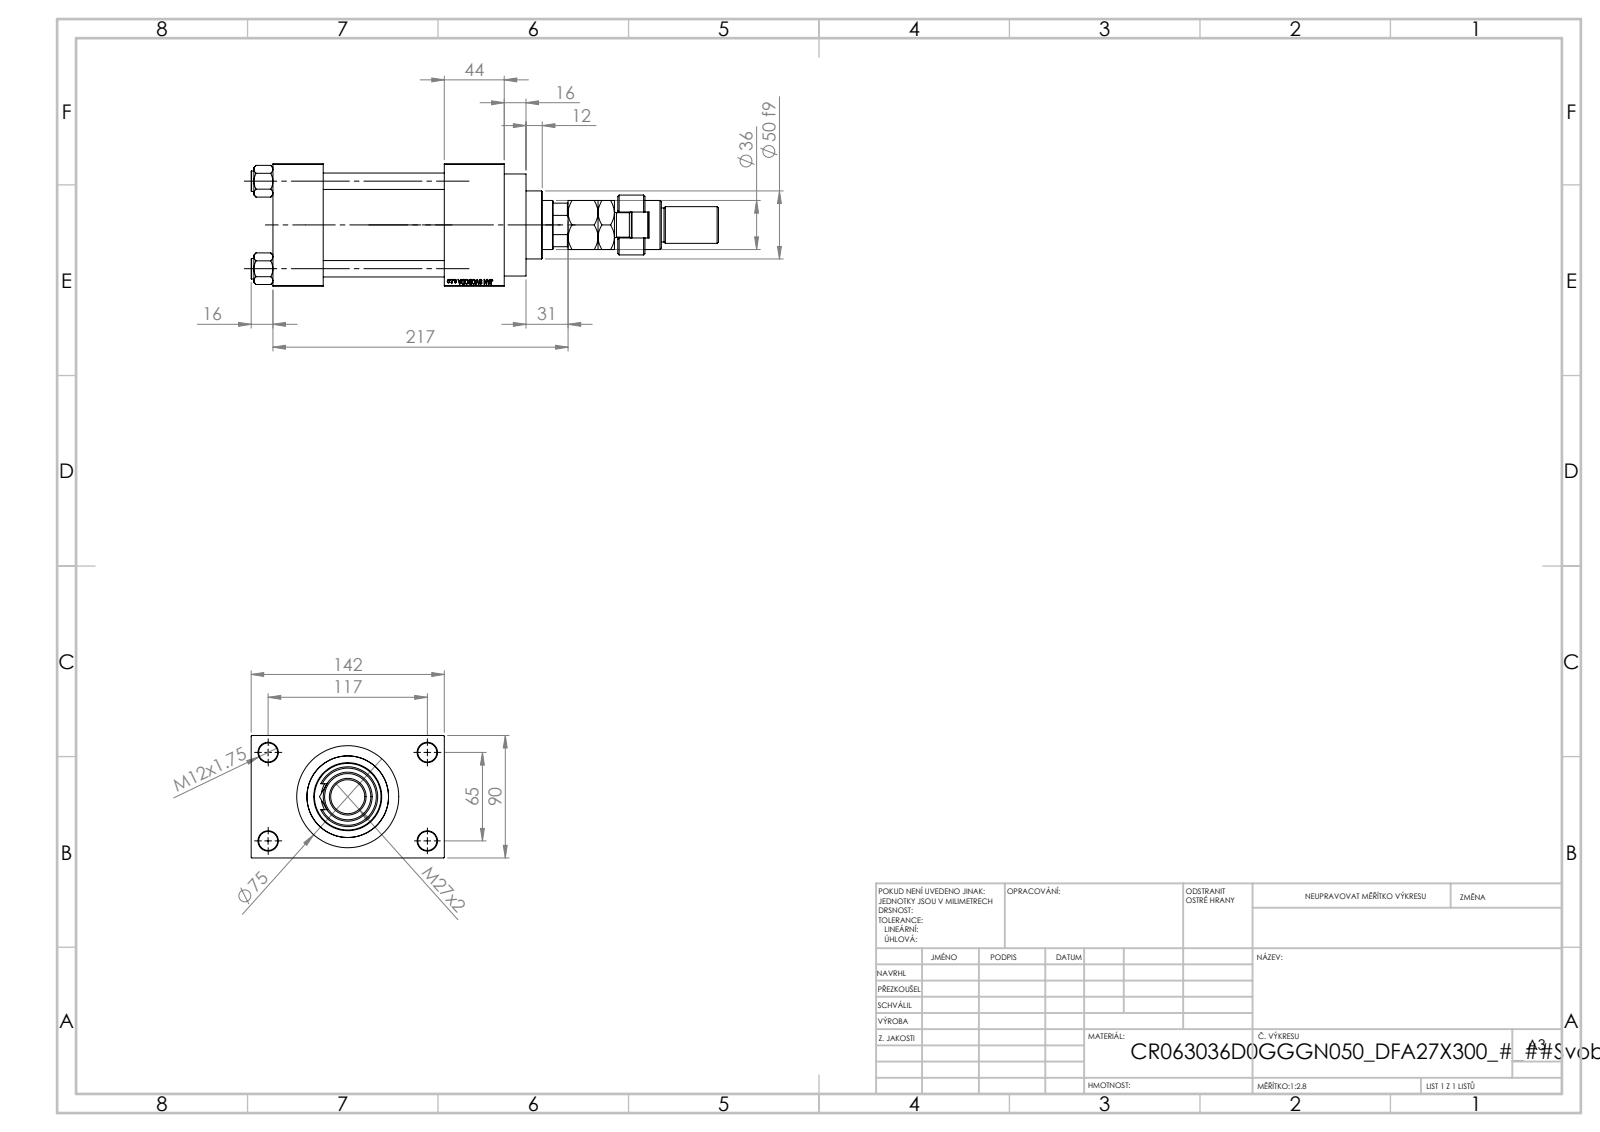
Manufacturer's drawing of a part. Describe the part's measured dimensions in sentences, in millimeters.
The part is named "V215CR_D_TYCINKA; V215CR_D_Body; V215_VC_A; NUT_M5_D (+3 more)". Its 3-D file was written by "SolidWorks 2019 (CONFIG_CONTROL_DESIGN)". It is 13 solids with 1189 faces: 525 planar, 102 cylindrical and 562 other. Overall it measures 343.5 by 142 by 90 millimeters. Its volume is 1 282 000 cubic millimeters and its surface area 245 554 square millimeters. Round holes: 4 of diameter 12, 4 of diameter 14, 2 of diameter 7, 2 of diameter 20.96, 2 of diameter 30, 1 of diameter 25.5, 1 of diameter 39, 1 of diameter 50, 1 of diameter 60, 1 of diameter 63. Round bosses or shafts: 4 of diameter 15, 1 of diameter 75, 1 of diameter 69, 1 of diameter 44, 1 of diameter 36, 1 of diameter 28, 1 of diameter 27, 1 of diameter 25. Partial cylindrical surfaces (rounded edges, fillets, slot ends): 1 of radius 9.5, 1 of radius 15, 1 of radius 17.5. The main face-to-face distances are 90, 89, 37, 126, 170, 133, 44, 26, 116, 142. The hole center spacings are 26.35, 45.47, 64.3, 66.92, 69.81, 90.65, 111.34, 65.
